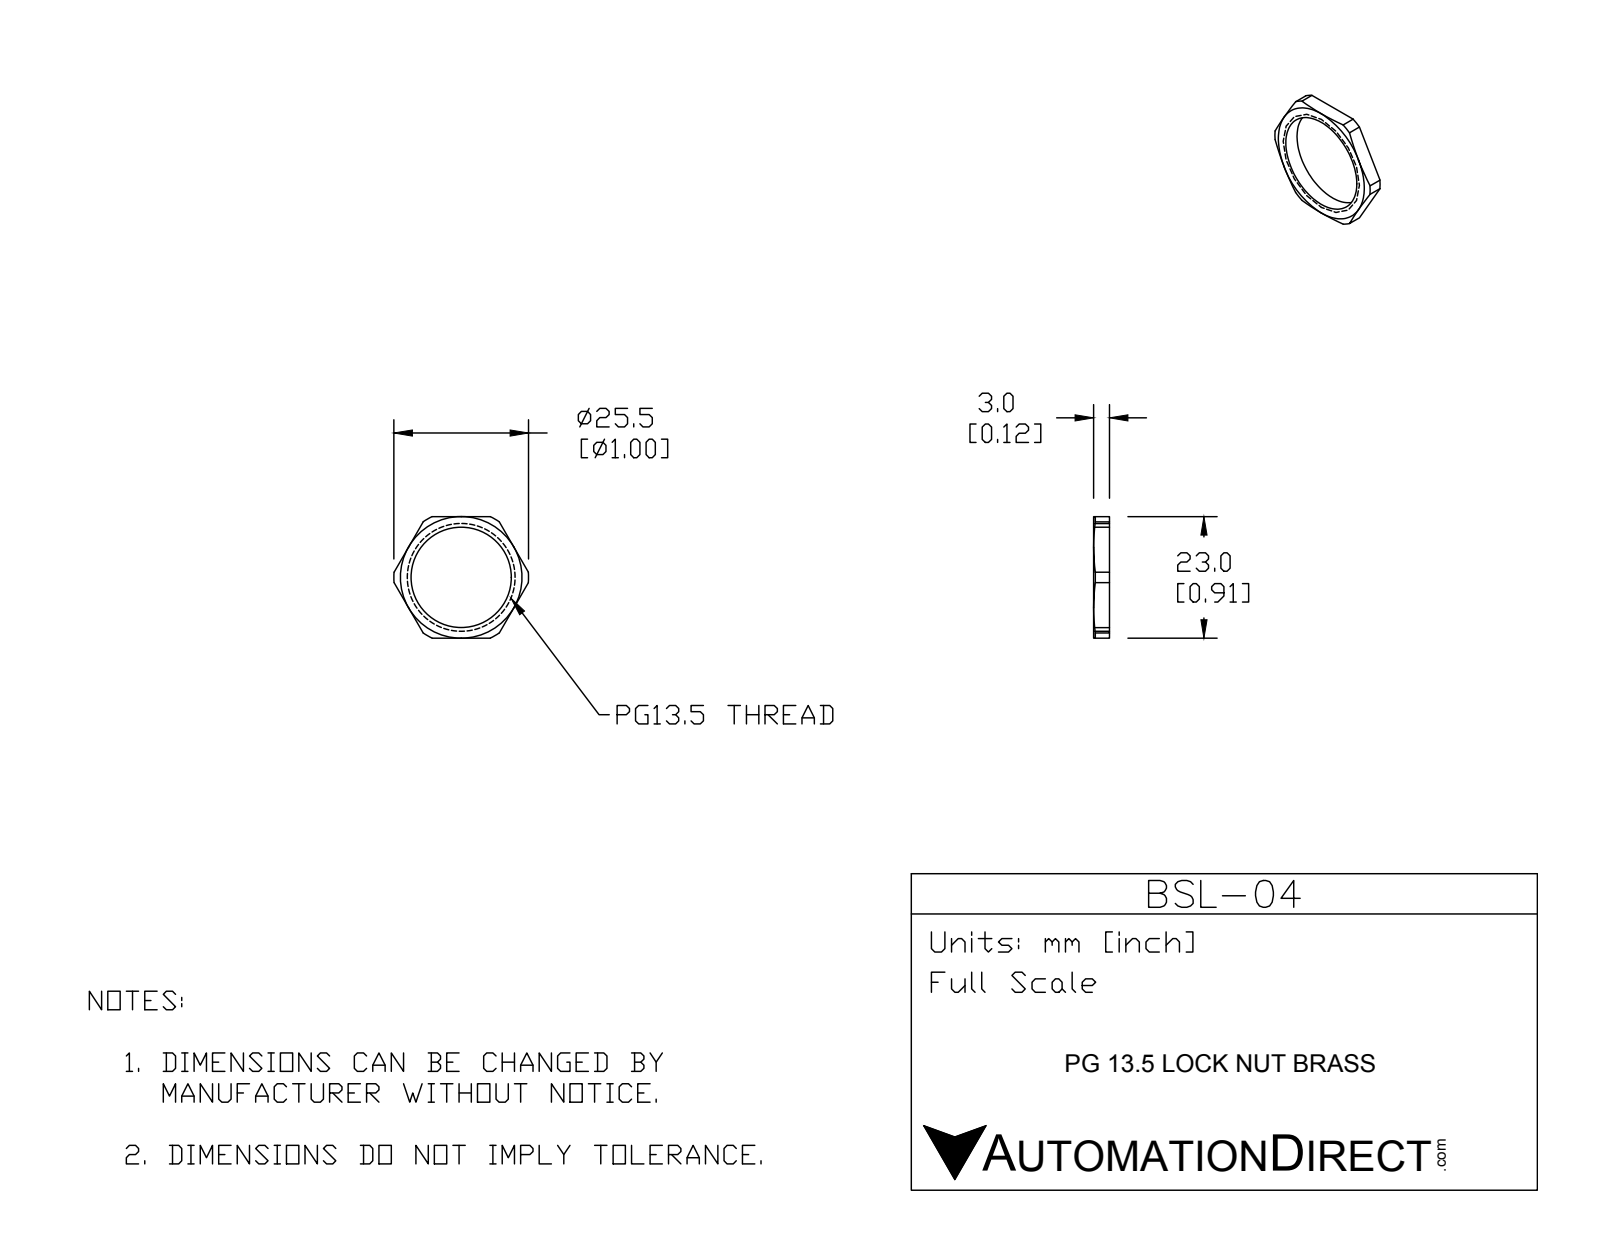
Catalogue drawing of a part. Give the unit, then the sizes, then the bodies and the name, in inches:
Units: inches
Overall size (bounding box): 1.004 × 0.906 × 0.118
Round holes (diameter × count): ⌀0.748 ×1
Partial cylindrical surfaces — rounded edges, fillets, slot ends (radius × count): R0.502 ×1
Main face-to-face distances: 0.118, 0.906
Volume: 0.031 in³ · Surface area: 1.16 in²
Bodies: 1 solid, 23 faces (8 planar, 9 cylindrical, 6 other)
Part name (STEP PRODUCT): BSL-04
STEP written by: SolidWorks 2015 (CONFIG_CONTROL_DESIGN)
